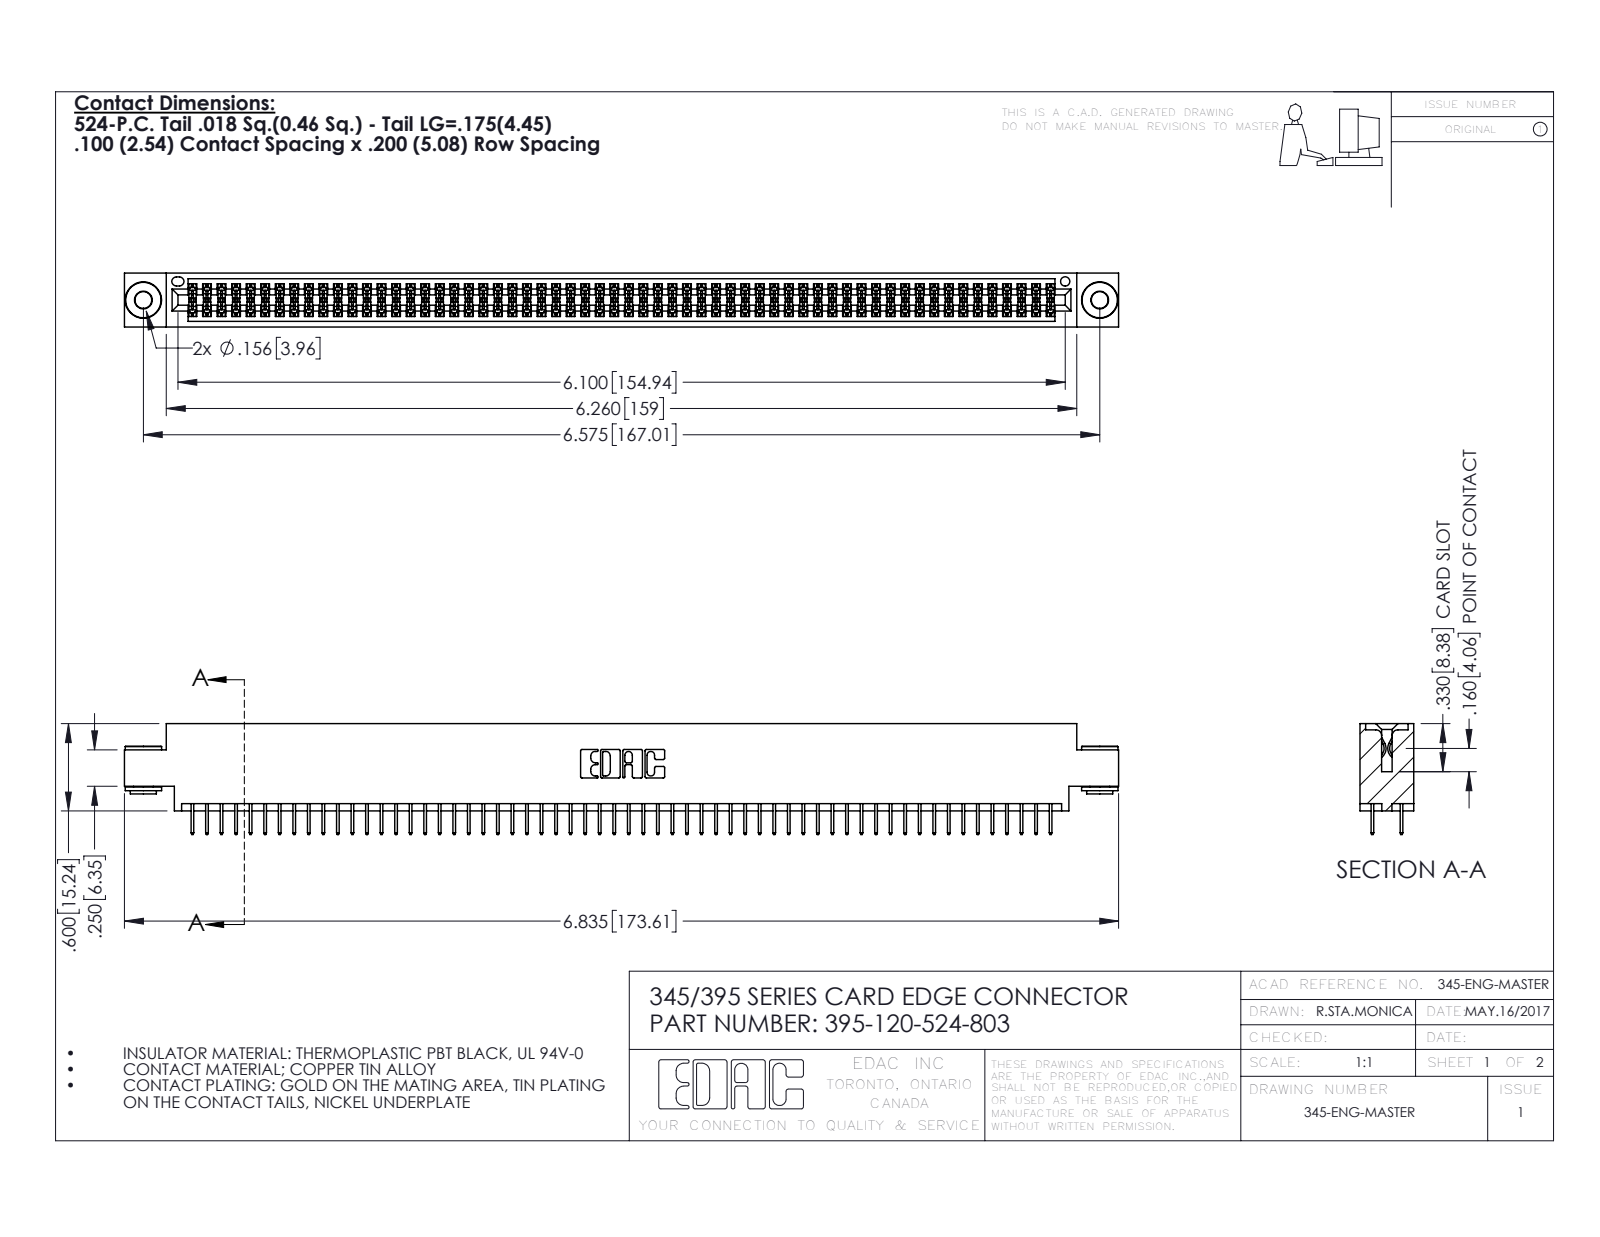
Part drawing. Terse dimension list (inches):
name: 395-120-524-803; 345 Part_0.170 Offset - 0.156 Dia-TH; 345-250-002_345-250-002-102; 345-292-001_345-293-124
written by: SolidWorks 2016 (CONFIG_CONTROL_DESIGN)
unit: in
bodies: 123 solids, 6648 faces (4774 planar, 1866 cylindrical, 8 other)
size: 6.835 × 0.762 × 0.37
volume: 1.023 in³; area: 38.73 in²
holes: 2× ⌀0.116, 2× ⌀0.156, 1× ⌀0.064
bosses: 2× ⌀0.25, 2× ⌀0.18, 2× ⌀0.136
rounds: 180× R0.006, 22× R0.01, 6× R0.007, 6× R0.031, 3× R0.026, 2× R0.014, 2× R0.019, 2× R0.022
face distances: 0.072, 0.298, 0.37, 0.2, 0.098, 0.272, 0.025, 0.225, 0.175, 0.072
hole spacings: 0.27, 6.339, 6.575
